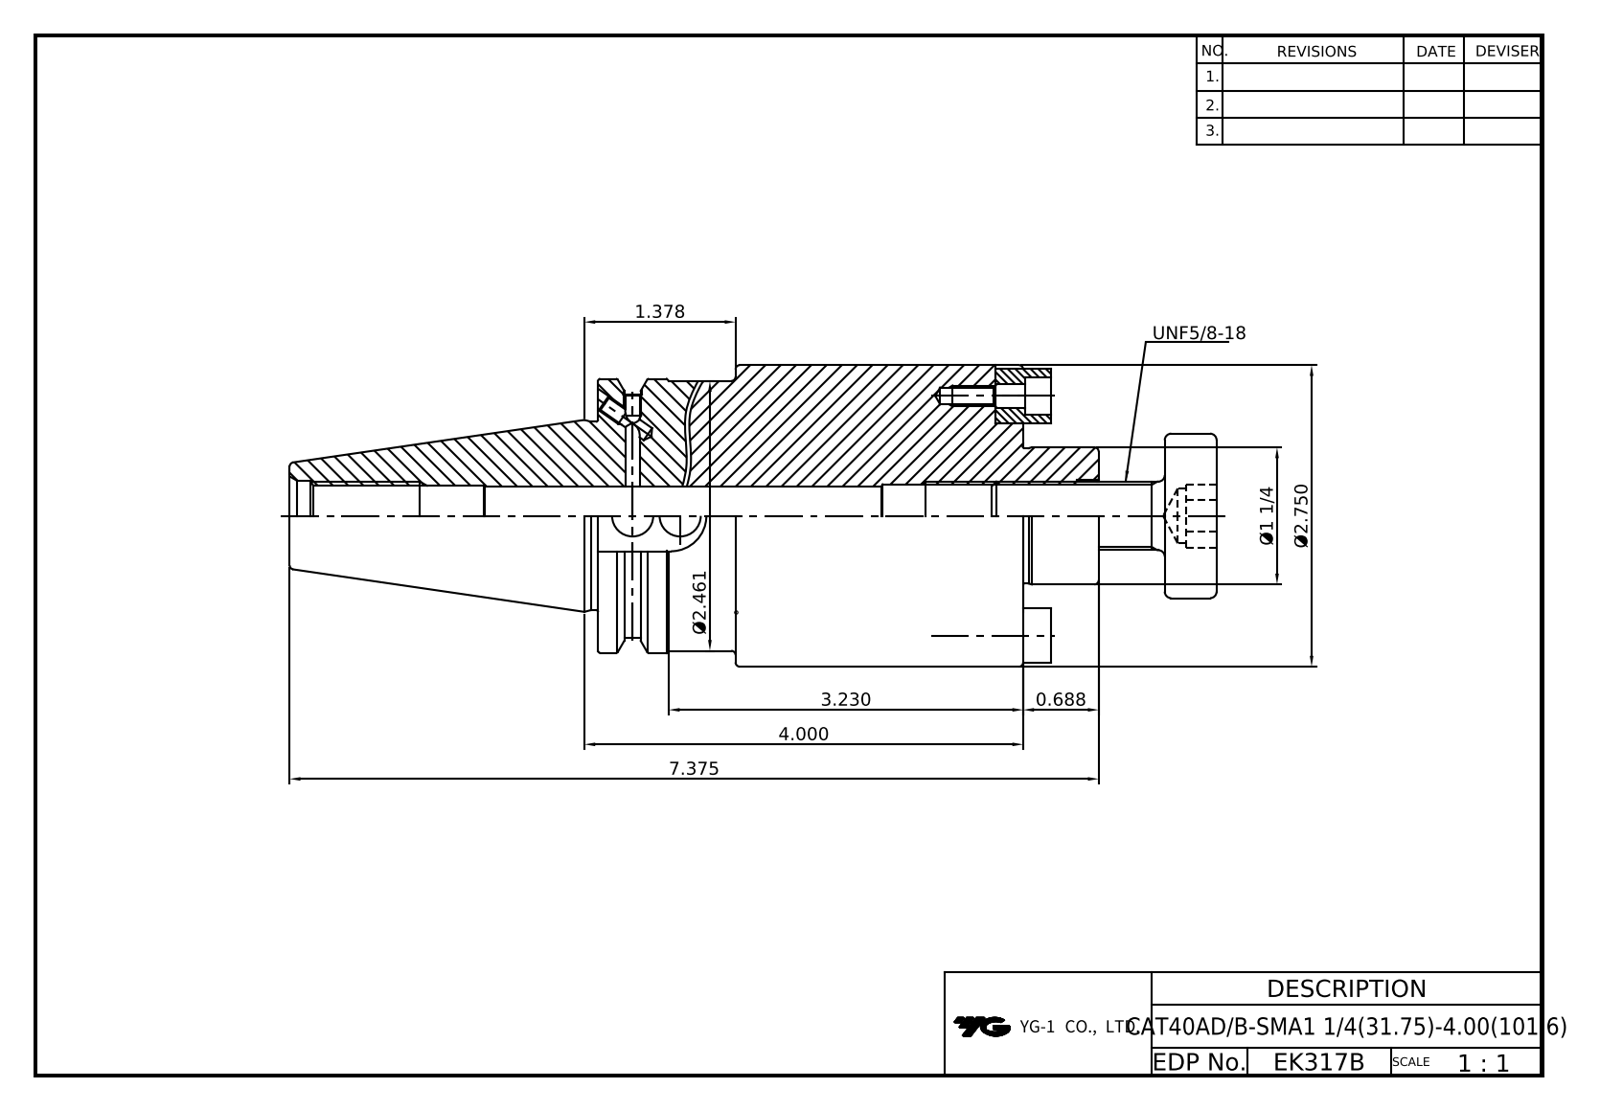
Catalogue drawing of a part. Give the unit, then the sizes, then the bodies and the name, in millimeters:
Units: millimetres
Overall size (bounding box): 214.3 × 69.9 × 69.9
Round holes (diameter × count): ⌀3.3 ×4, ⌀3.7 ×2, ⌀4 ×2, ⌀4.2 ×2, ⌀5.5 ×2, ⌀8.7 ×2, ⌀9.5 ×1, ⌀12.7 ×1, ⌀13 ×1, ⌀13.4 ×1, ⌀14.4 ×1, ⌀16.3 ×1
Round bosses / shafts (diameter × count): ⌀7.9 ×2, ⌀4.8 ×2, ⌀69.9 ×1, ⌀63.5 ×1, ⌀62.5 ×1, ⌀43.6 ×1, ⌀38.1 ×1, ⌀31.8 ×1
Partial cylindrical surfaces — rounded edges, fillets, slot ends (radius × count): R6.4 ×2, R8.2 ×1, R28.1 ×1
Main face-to-face distances: 98.4, 142.9, 44.5, 130.9, 32.4, 12, 6.4, 12.7, 31.8, 66.6
Hole centre spacings: 27.8, 27.8, 55.5, 55.5, 55.5
Volume: 423 100 mm³ · Surface area: 56 050 mm²
Bodies: 6 solids, 173 faces (84 planar, 49 cylindrical, 40 other)
Part name (STEP PRODUCT): LO-CAT40ADB-SMA31.75-101.6; HEX'' WRENCH BOLT-UNC#10-24x1_2L; DRIVE KEY-12.7x12.7x12.7; COLLAR BOLT-UNF5_8-18x40L
STEP written by: Autodesk Inventor 2022 (AUTOMOTIVE_DESIGN)
